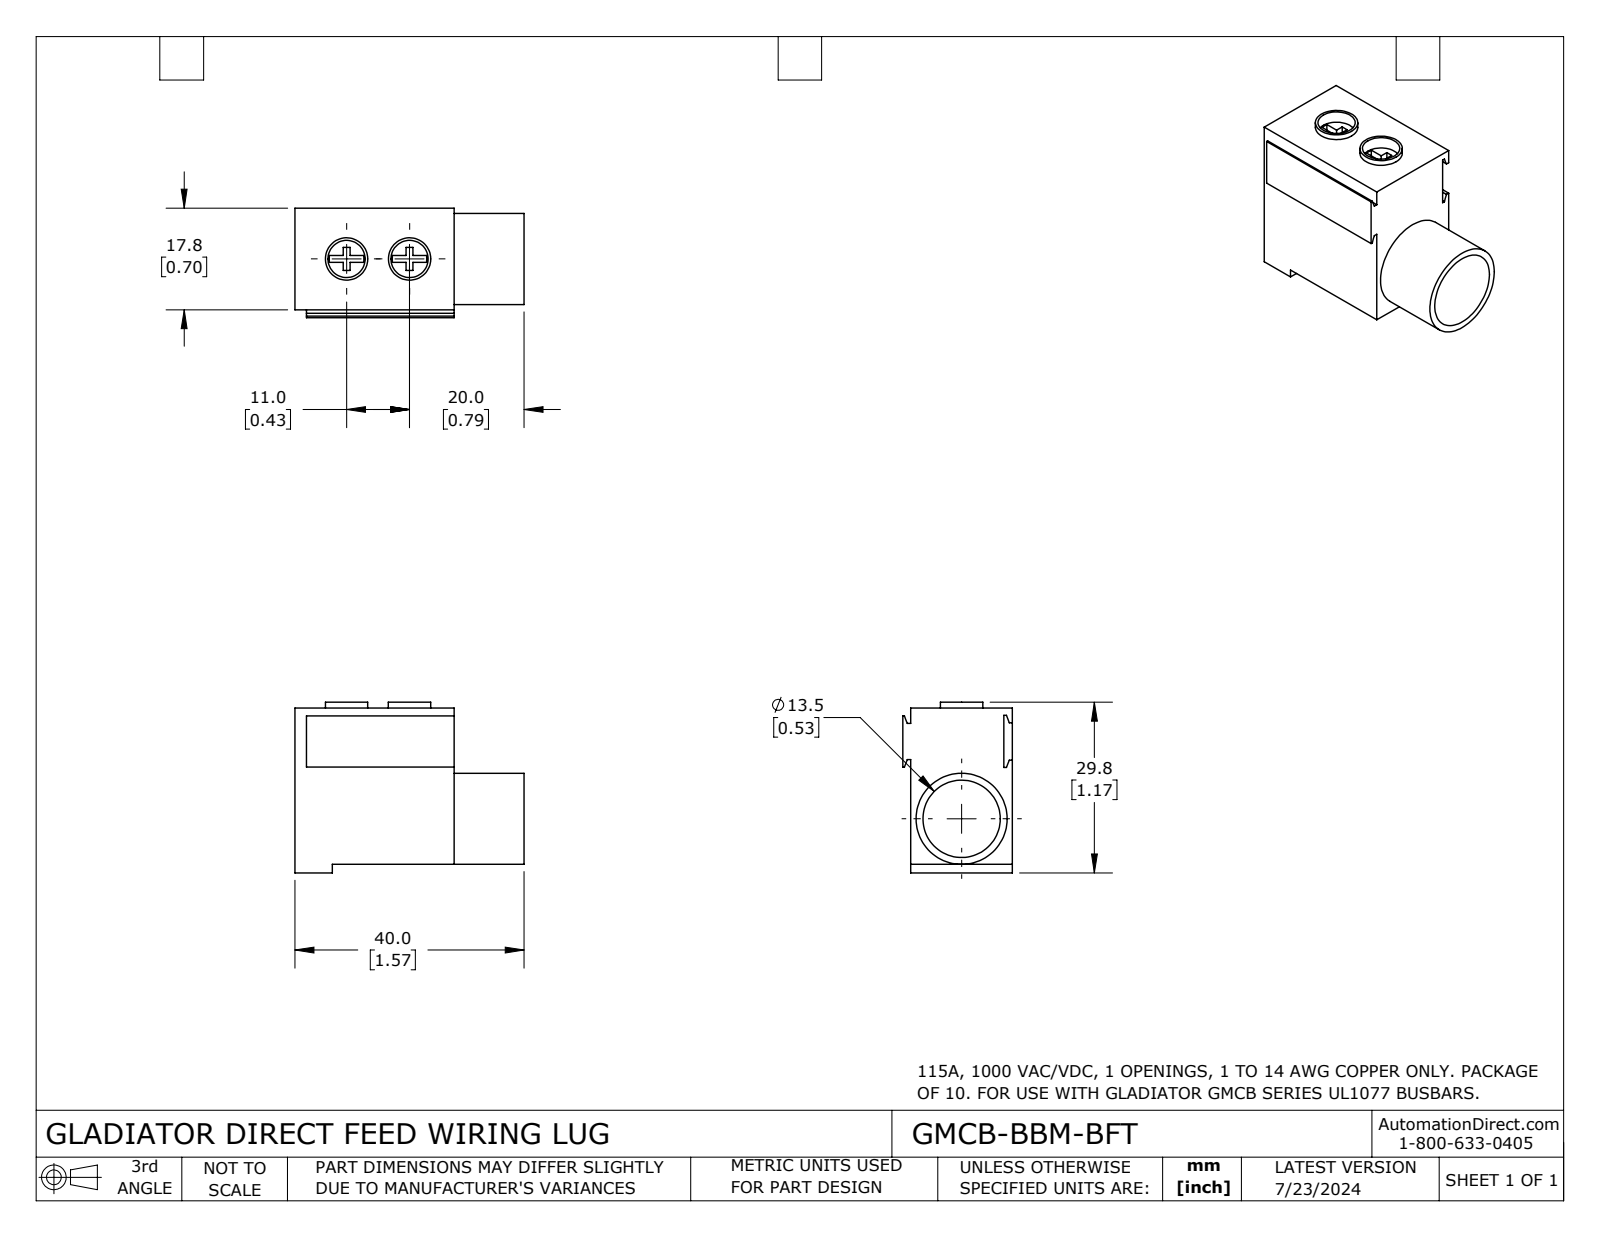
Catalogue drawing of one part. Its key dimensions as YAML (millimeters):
part_name: "GMCB-BBM-BFT"
step_written_by: "SolidWorks 2023 (CONFIG_CONTROL_DESIGN)"
units: millimeters
bodies: {solids: 1, faces: 83, planar: 71, cylindrical: 12, other: 0}
overall_size: [40, 29.8, 19.2]
volume: 13800
surface_area: 5449
round_holes:
  - {diameter: 6.5, count: 2}
  - {diameter: 13.5, count: 1}
round_bosses_or_shafts:
  - {diameter: 7.4, count: 2}
  - {diameter: 15.9, count: 1}
face_to_face_distances: [17.8, 1.5, 27.3, 27.8, 1.4, 16.3, 17.7, 19.2, 1.2, 24.6]
hole_center_spacings: [11]
